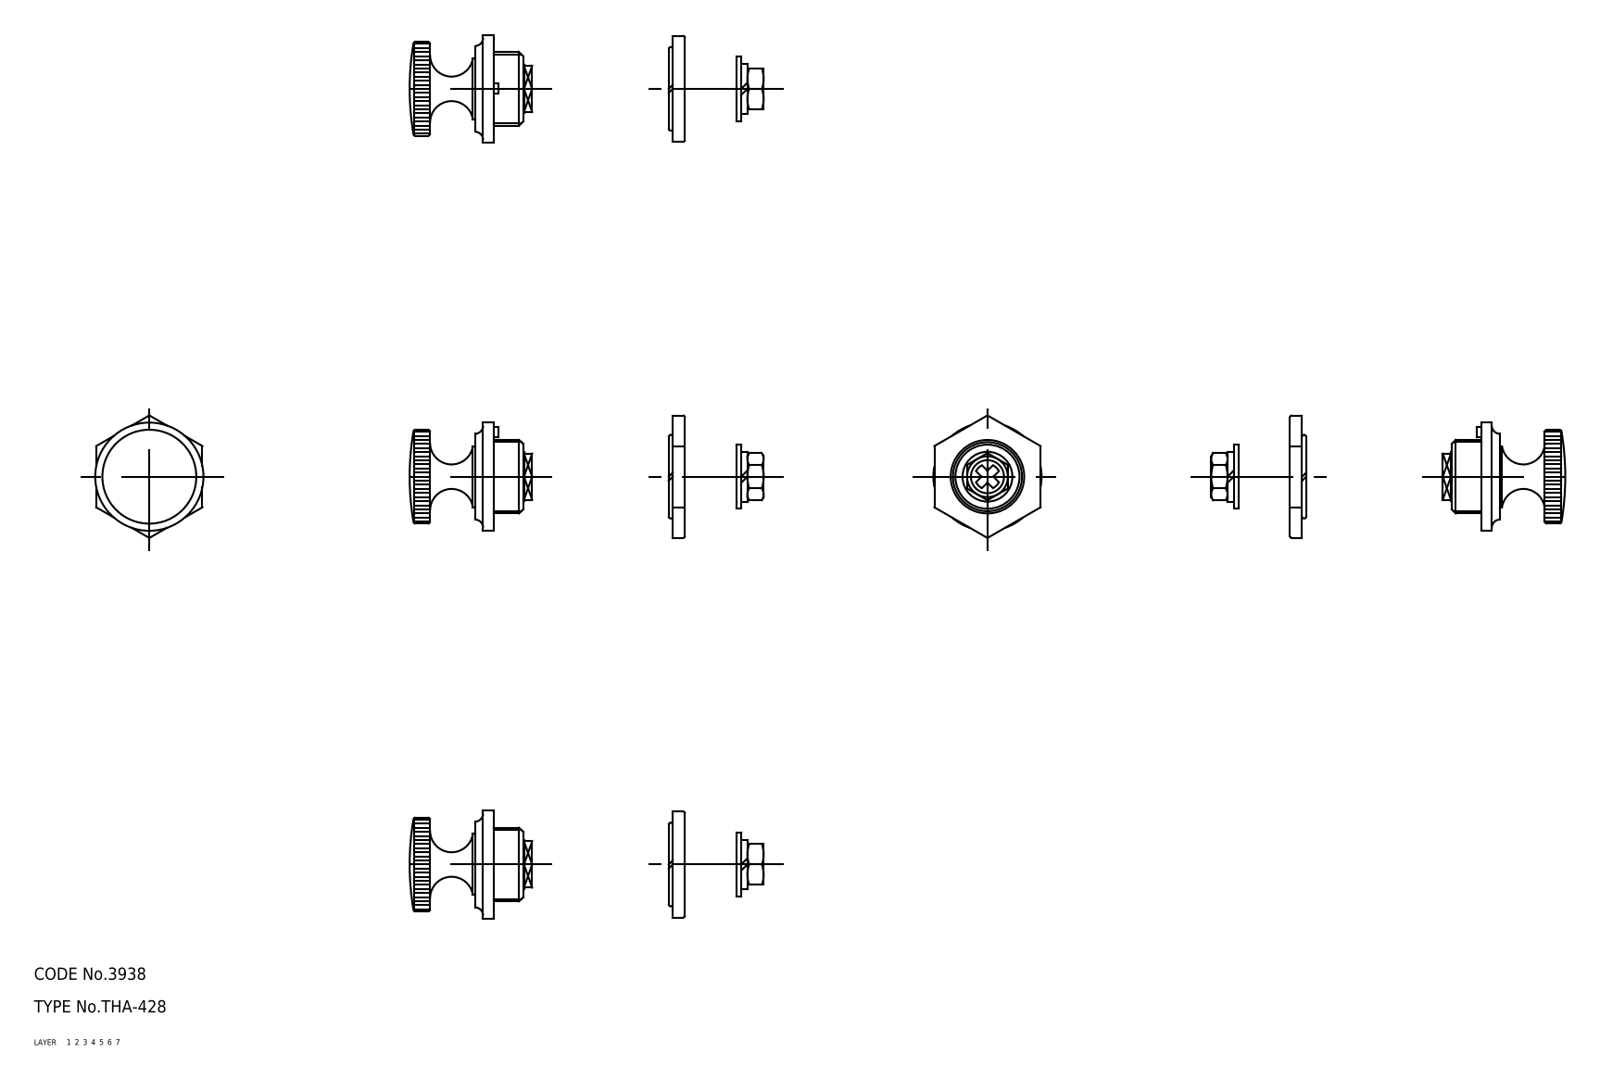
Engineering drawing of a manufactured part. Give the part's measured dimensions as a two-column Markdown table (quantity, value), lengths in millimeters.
| quantity | value |
| --- | --- |
| part name | konb; washer_A; nut; bolt (+1 more) |
| STEP written by | CADfix (AUTOMOTIVE_DESIGN) |
| units | millimeters |
| bodies | 5 solids, 105 faces (0 planar, 0 cylindrical, 105 other) |
| overall size | 36.7 × 30.02 × 26.5 |
| volume | 8 190 mm³ |
| surface area | 6 390 mm² |
